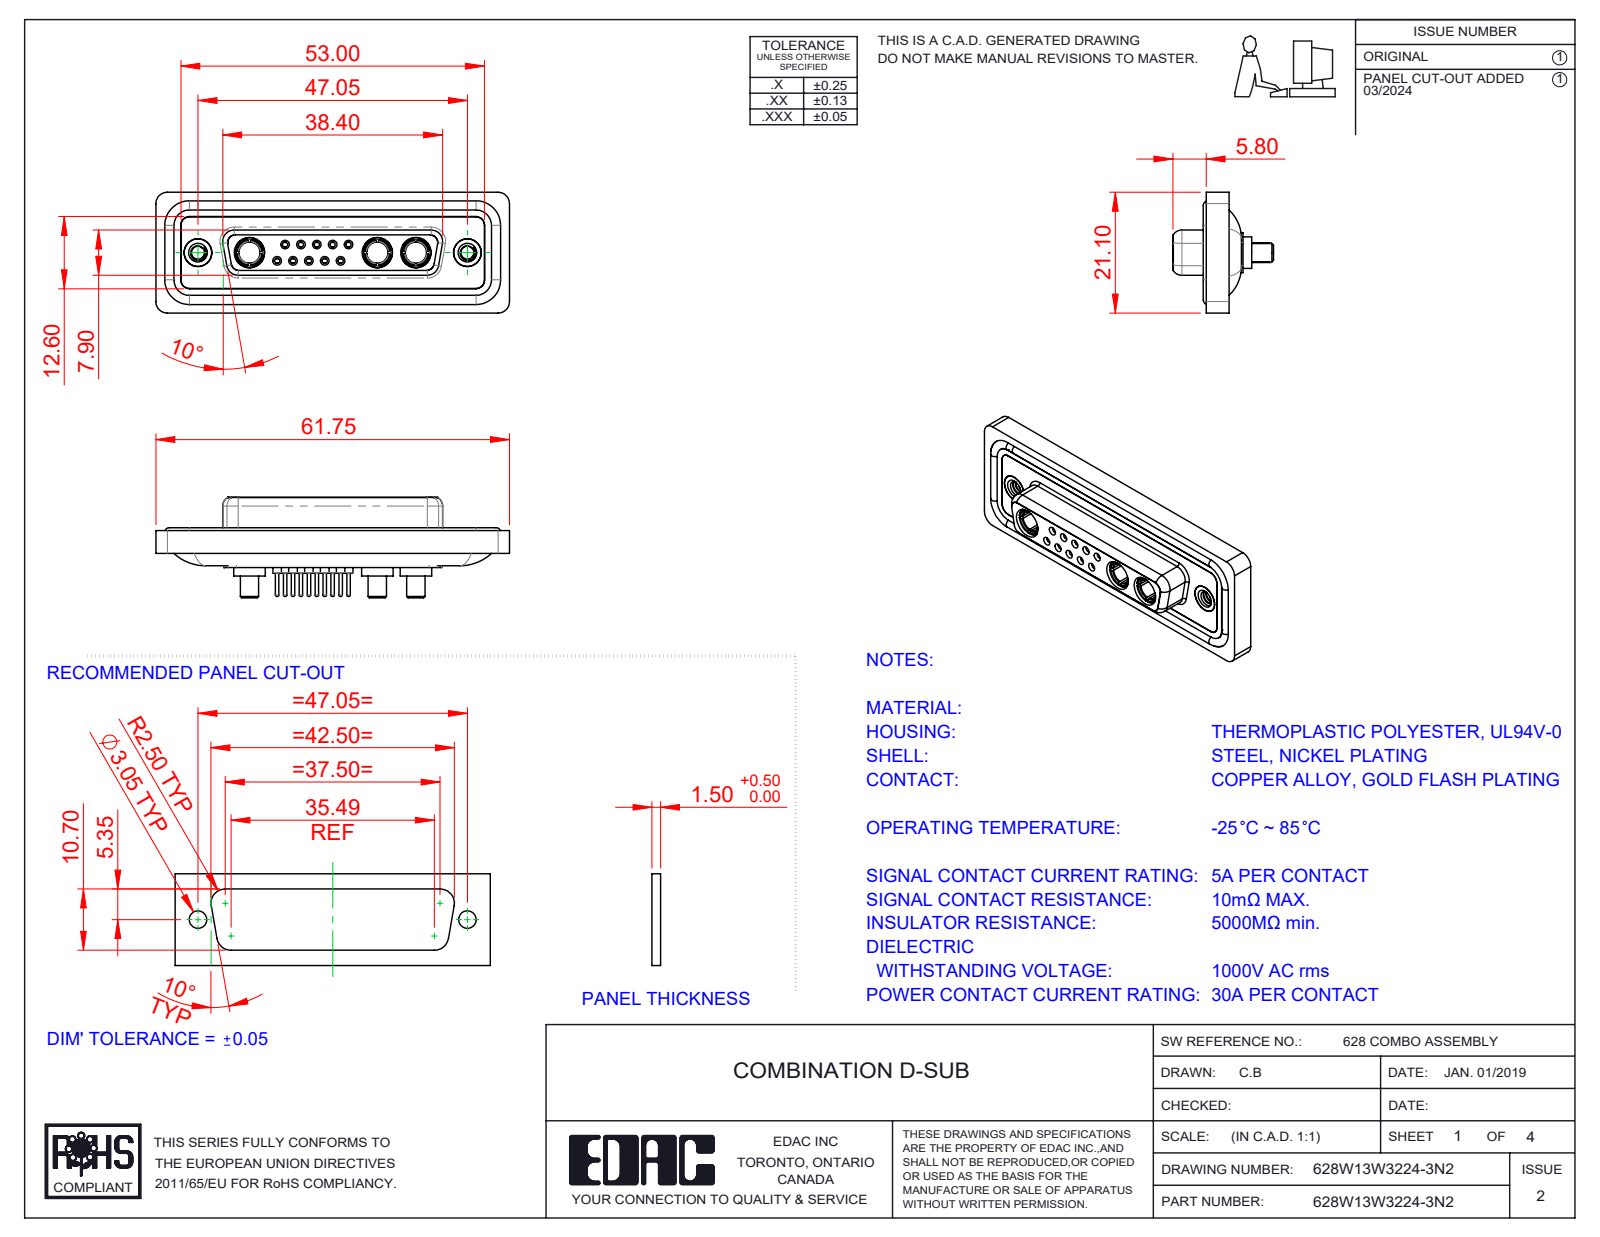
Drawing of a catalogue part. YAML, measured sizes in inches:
part_name: "Power Socket_30A S; 628Combo Waterproof Housing_25 Contacts; 628Combo Threaded Rivet_2; 628Combo Contact Row 2_24 (+5 more)"
step_written_by: "SolidWorks 2023 (CONFIG_CONTROL_DESIGN)"
units: inches
bodies: {solids: 23, faces: 1158, planar: 342, cylindrical: 447, other: 369}
overall_size: [2.431, 0.831, 0.691]
volume: 0.506
surface_area: 21.27
round_holes:
  - {diameter: 0.035, count: 10}
  - {diameter: 0.043, count: 10}
  - {diameter: 0.059, count: 10}
  - {diameter: 0.079, count: 10}
  - {diameter: 0.063, count: 5}
  - {diameter: 0.067, count: 5}
  - {diameter: 0.191, count: 5}
  - {diameter: 0.146, count: 3}
  - {diameter: 0.209, count: 3}
  - {diameter: 0.089, count: 2}
  - {diameter: 0.157, count: 2}
  - {diameter: 0.159, count: 2}
round_bosses_or_shafts:
  - {diameter: 0.087, count: 10}
  - {diameter: 0.024, count: 10}
  - {diameter: 0.063, count: 9}
  - {diameter: 0.217, count: 3}
  - {diameter: 0.205, count: 3}
  - {diameter: 0.195, count: 3}
  - {diameter: 0.187, count: 3}
  - {diameter: 0.148, count: 3}
partial_cylinders:
  - {radius: 0.059, count: 22}
  - {radius: 0.079, count: 18}
  - {radius: 0.053, count: 8}
  - {radius: 0.063, count: 8}
  - {radius: 0.01, count: 4}
  - {radius: 0.02, count: 4}
  - {radius: 0.024, count: 4}
  - {radius: 0.026, count: 4}
face_to_face_distances: [0.016, 0.071, 0.293, 0.222, 0.02, 0.26, 0.278, 0.063, 0.114, 0.043]
hole_center_spacings: [0.124, 0.109, 0.198, 0.198, 0.218, 0.327, 0.295, 0.109]
